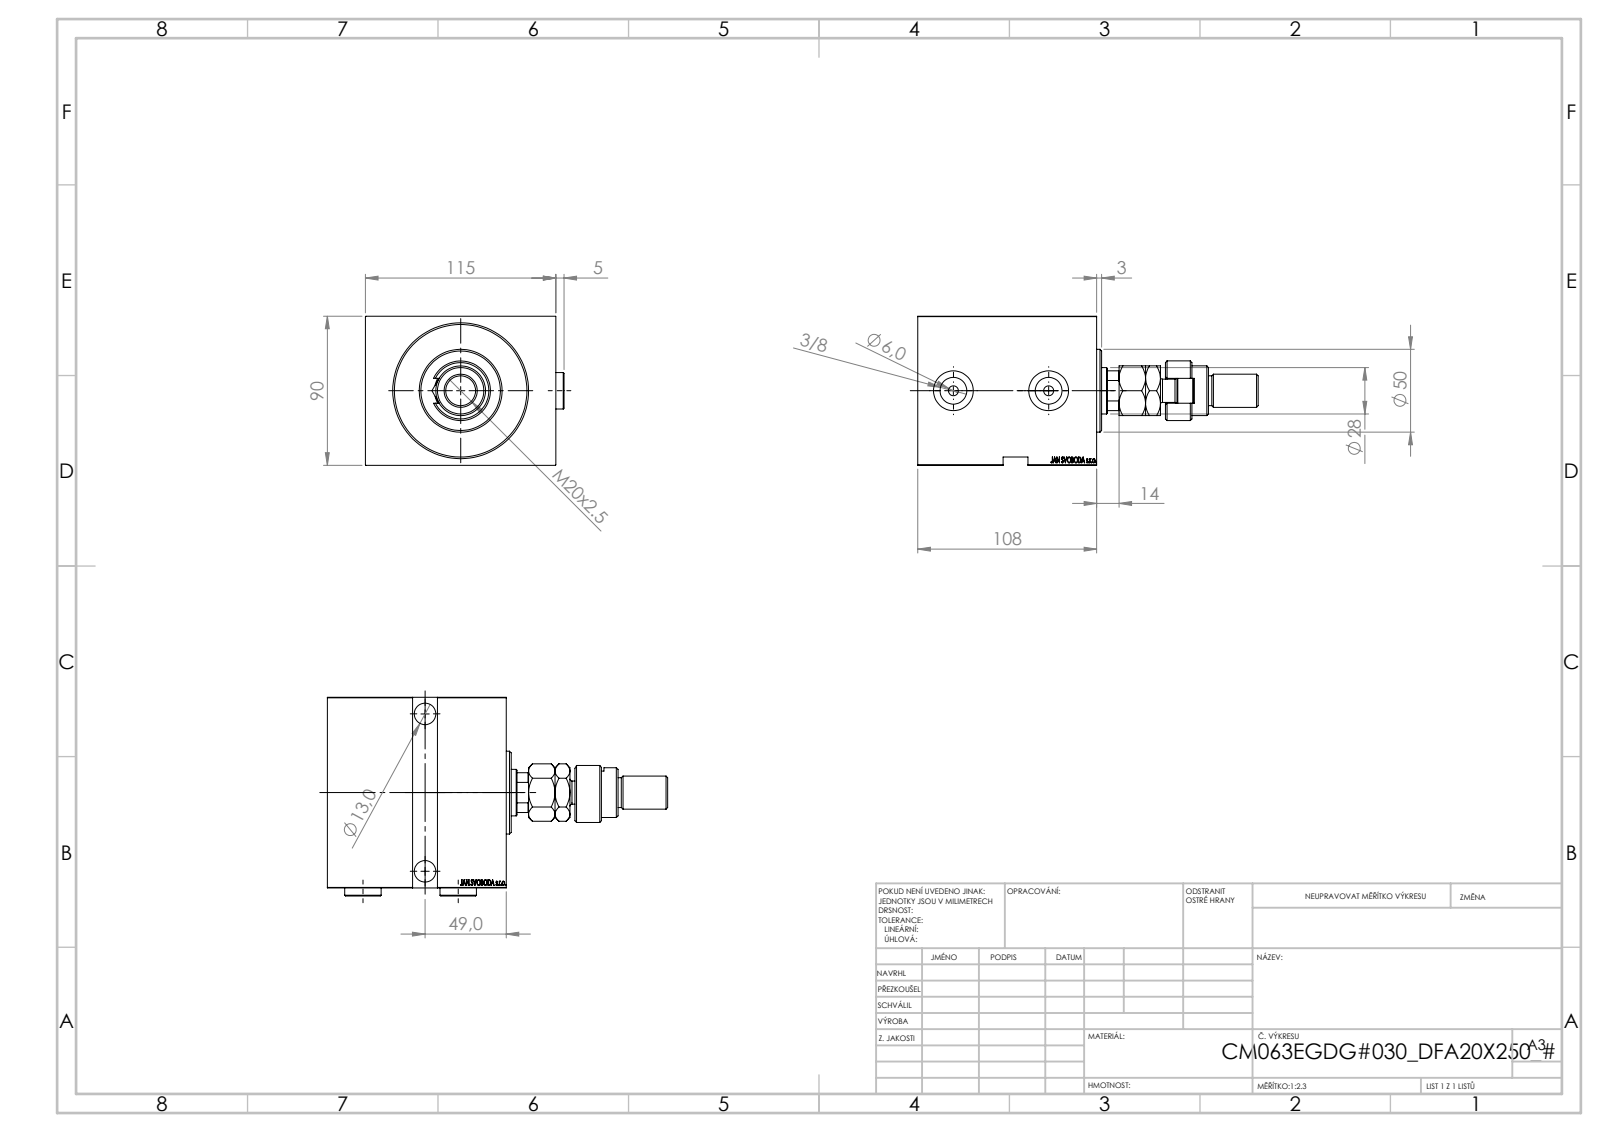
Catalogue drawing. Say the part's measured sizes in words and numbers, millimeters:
The part is named "MFA; V450CM_E_Body; V450CM_VC_B; V450CM_E_VCP (+2 more)". Its 3-D file was written by "SolidWorks 2019 (CONFIG_CONTROL_DESIGN)". It is 7 solids with 987 faces: 472 planar, 73 cylindrical and 442 other. Overall it measures 205.5 by 119.9 by 90 millimeters. Its volume is 1 059 000 cubic millimeters and its surface area 146 835 square millimeters. Round holes: 2 of diameter 6, 2 of diameter 13, 2 of diameter 16.17, 2 of diameter 19, 2 of diameter 24, 1 of diameter 18.5, 1 of diameter 28, 1 of diameter 31.5, 1 of diameter 63, 1 of diameter 80. Round bosses or shafts: 3 of diameter 22, 1 of diameter 65, 1 of diameter 50, 1 of diameter 36, 1 of diameter 30, 1 of diameter 20, 1 of diameter 18, 1 of diameter 14. Partial cylindrical surfaces (rounded edges, fillets, slot ends): 1 of radius 7.5, 1 of radius 12, 1 of radius 13.5. The main face-to-face distances are 90, 115, 108, 17.5, 90.5, 5, 38.5, 103, 85.5, 43.5. The hole center spacings are 57.5, 95.
